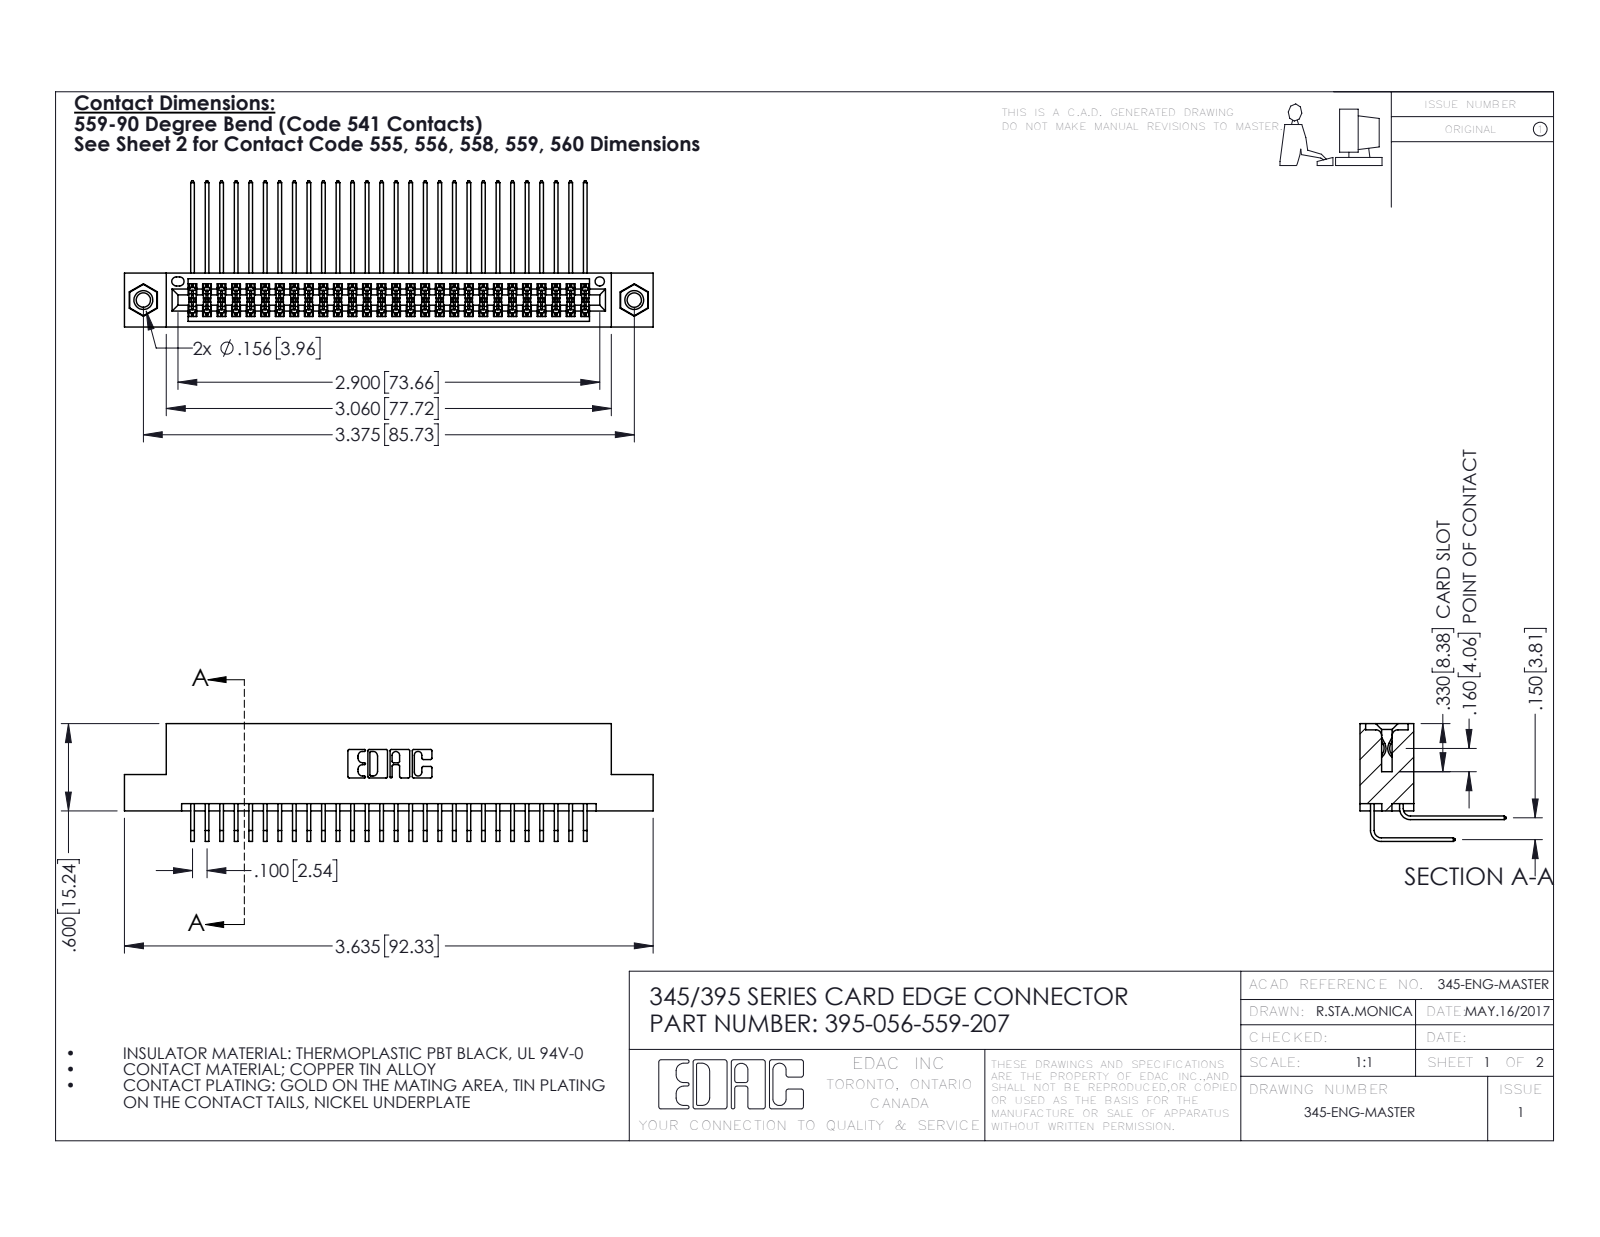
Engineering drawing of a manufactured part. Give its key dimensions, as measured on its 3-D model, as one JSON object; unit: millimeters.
{"part_name": "345-292-001_558 559 Tail - 1; 345-250-001_345-250-005-103; 395-056-559-207; 345-292-001_559 Tail - 2 (+1 more)", "step_written_by": "SolidWorks 2016 (CONFIG_CONTROL_DESIGN)", "units": "millimeters", "bodies": {"solids": 59, "faces": 3098, "planar": 2072, "cylindrical": 1010, "other": 16}, "overall_size": [92.3, 25.5, 20.5], "volume_mm3": 9140, "surface_area_mm2": 14800, "round_holes": [[2.5, 2], [3.2, 2], [4, 2], [1.6, 1]], "round_bosses_or_shafts": [[3.9, 2]], "partial_cylinders_radius": [[0.2, 111], [0.3, 22], [0.2, 6], [0.8, 6], [0.7, 3], [0.4, 2], [0.5, 2], [0.6, 2]], "face_to_face_distances": [1.8, 7.6, 5.1, 9.4, 2.5, 6.9, 0.6, 5.7, 3.8, 4.4], "hole_center_spacings": [6.9, 79.8, 85.7]}
